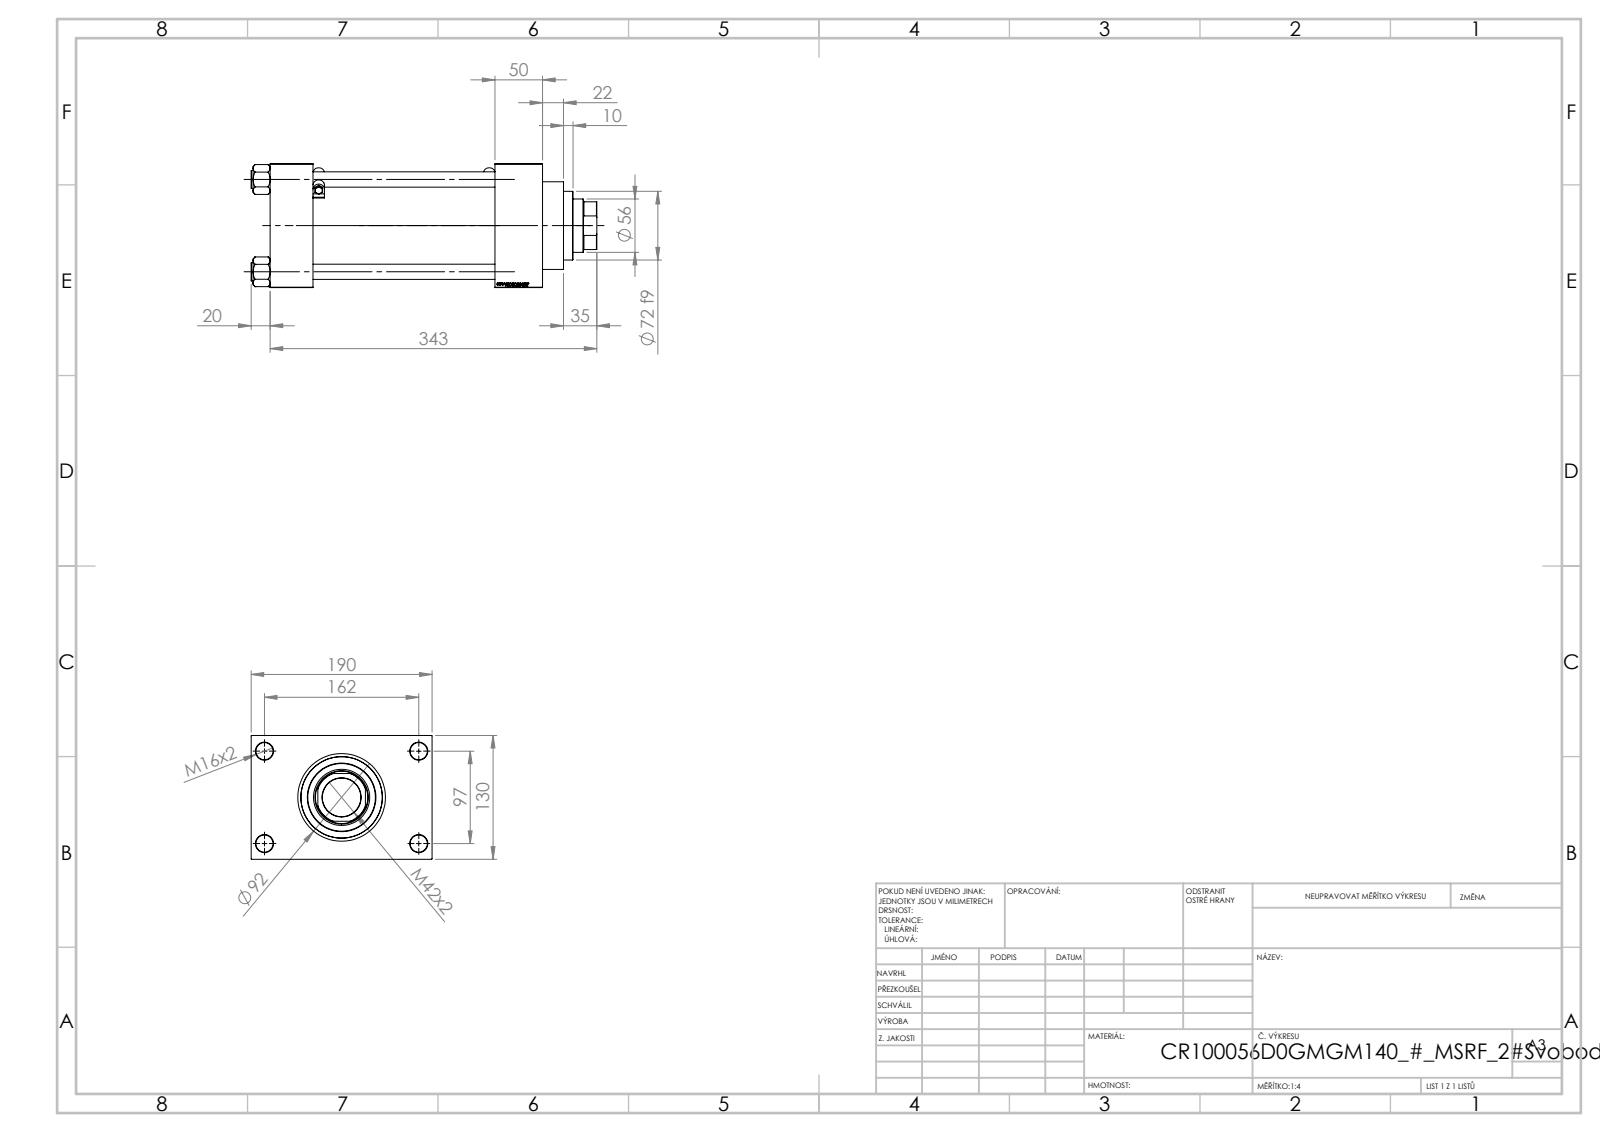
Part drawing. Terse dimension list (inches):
name: V215CR_D_Body; V215CR_VCP_D; NUT_M5_D; V215CR_D_TYCINKA (+2 more)
written by: SolidWorks 2019 (CONFIG_CONTROL_DESIGN)
unit: in
bodies: 13 solids, 1215 faces (581 planar, 116 cylindrical, 518 other)
size: 14.291 × 7.48 × 5.118
volume: 191.9 in³; area: 759.2 in²
holes: 4× ⌀0.63, 4× ⌀0.709, 2× ⌀0.276, 2× ⌀1.041, 2× ⌀1.378, 1× ⌀1.594, 1× ⌀2.205, 1× ⌀2.323, 1× ⌀2.992, 1× ⌀3.366, 1× ⌀3.937
bosses: 4× ⌀0.748, 2× ⌀0.197, 2× ⌀0.098, 1× ⌀4.173, 1× ⌀3.622, 1× ⌀2.835
rounds: 12× R0.02, 4× R0.236, 1× R1.063
face distances: 5.118, 1.969, 1.772, 9.291, 7.52, 11.26, 9.488, 1.181, 7.48, 6.299
hole spacings: 1.281, 2.698, 3.717, 3.815, 4.026, 5.096, 6.367, 3.819
